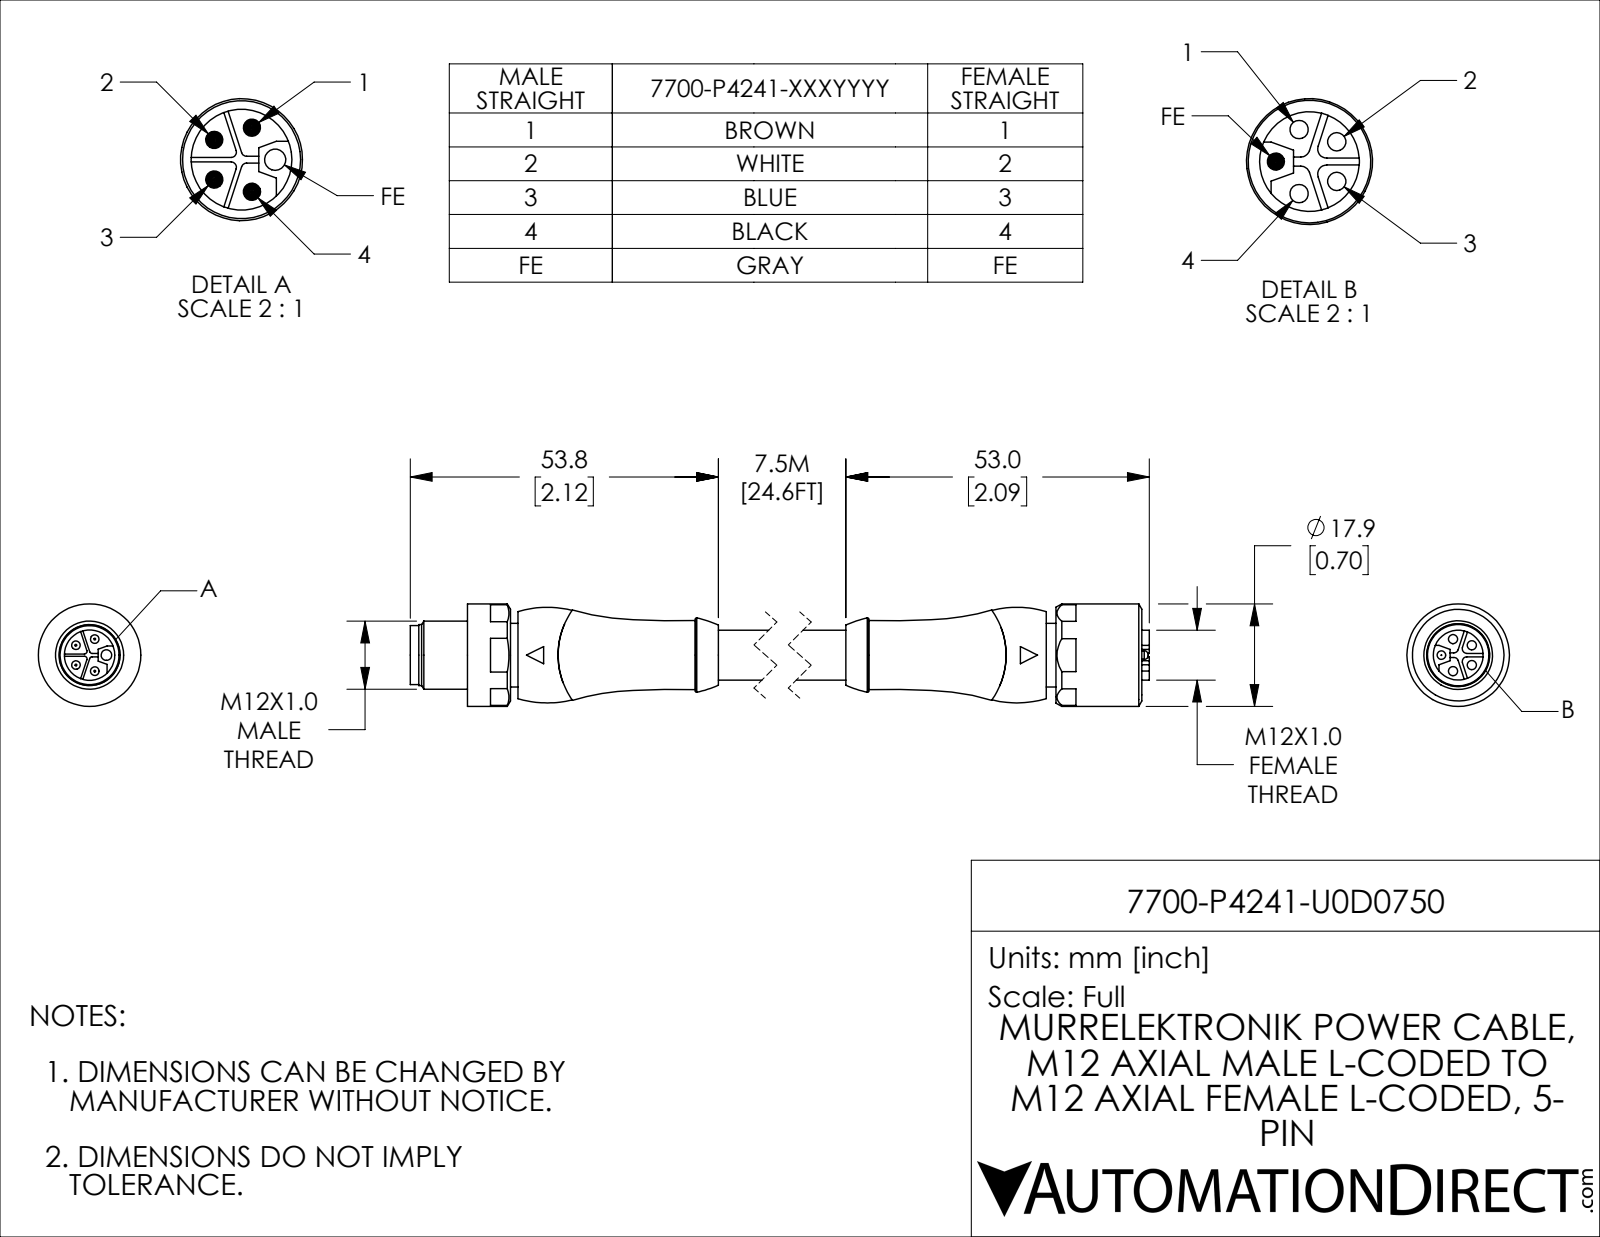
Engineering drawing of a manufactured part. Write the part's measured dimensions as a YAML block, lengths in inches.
part_name: "7700-P4241-U0D0750_2; 7700-P4241-U0D0750; 7700-P4241-U0D0750_1"
step_written_by: "SolidWorks 2021 (CONFIG_CONTROL_DESIGN)"
units: inches
bodies: {solids: 3, faces: 214, planar: 98, cylindrical: 62, other: 54}
overall_size: [5.386, 0.705, 0.705]
volume: 1.09
surface_area: 14.44
round_holes:
  - {diameter: 0.063, count: 4}
  - {diameter: 0.073, count: 1}
  - {diameter: 0.346, count: 1}
  - {diameter: 0.433, count: 1}
  - {diameter: 0.512, count: 1}
round_bosses_or_shafts:
  - {diameter: 0.059, count: 5}
  - {diameter: 0.705, count: 1}
  - {diameter: 0.51, count: 1}
  - {diameter: 0.469, count: 1}
  - {diameter: 0.437, count: 1}
  - {diameter: 0.419, count: 1}
  - {diameter: 0.406, count: 1}
  - {diameter: 0.343, count: 1}
partial_cylinders:
  - {radius: 0.018, count: 4}
  - {radius: 0.031, count: 4}
face_to_face_distances: [4.283, 0.067, 0.346, 0.666, 0.051, 0.295, 0.228, 4.941, 0.657, 4.35]
hole_center_spacings: [0.116, 0.136, 0.22, 0.22]
